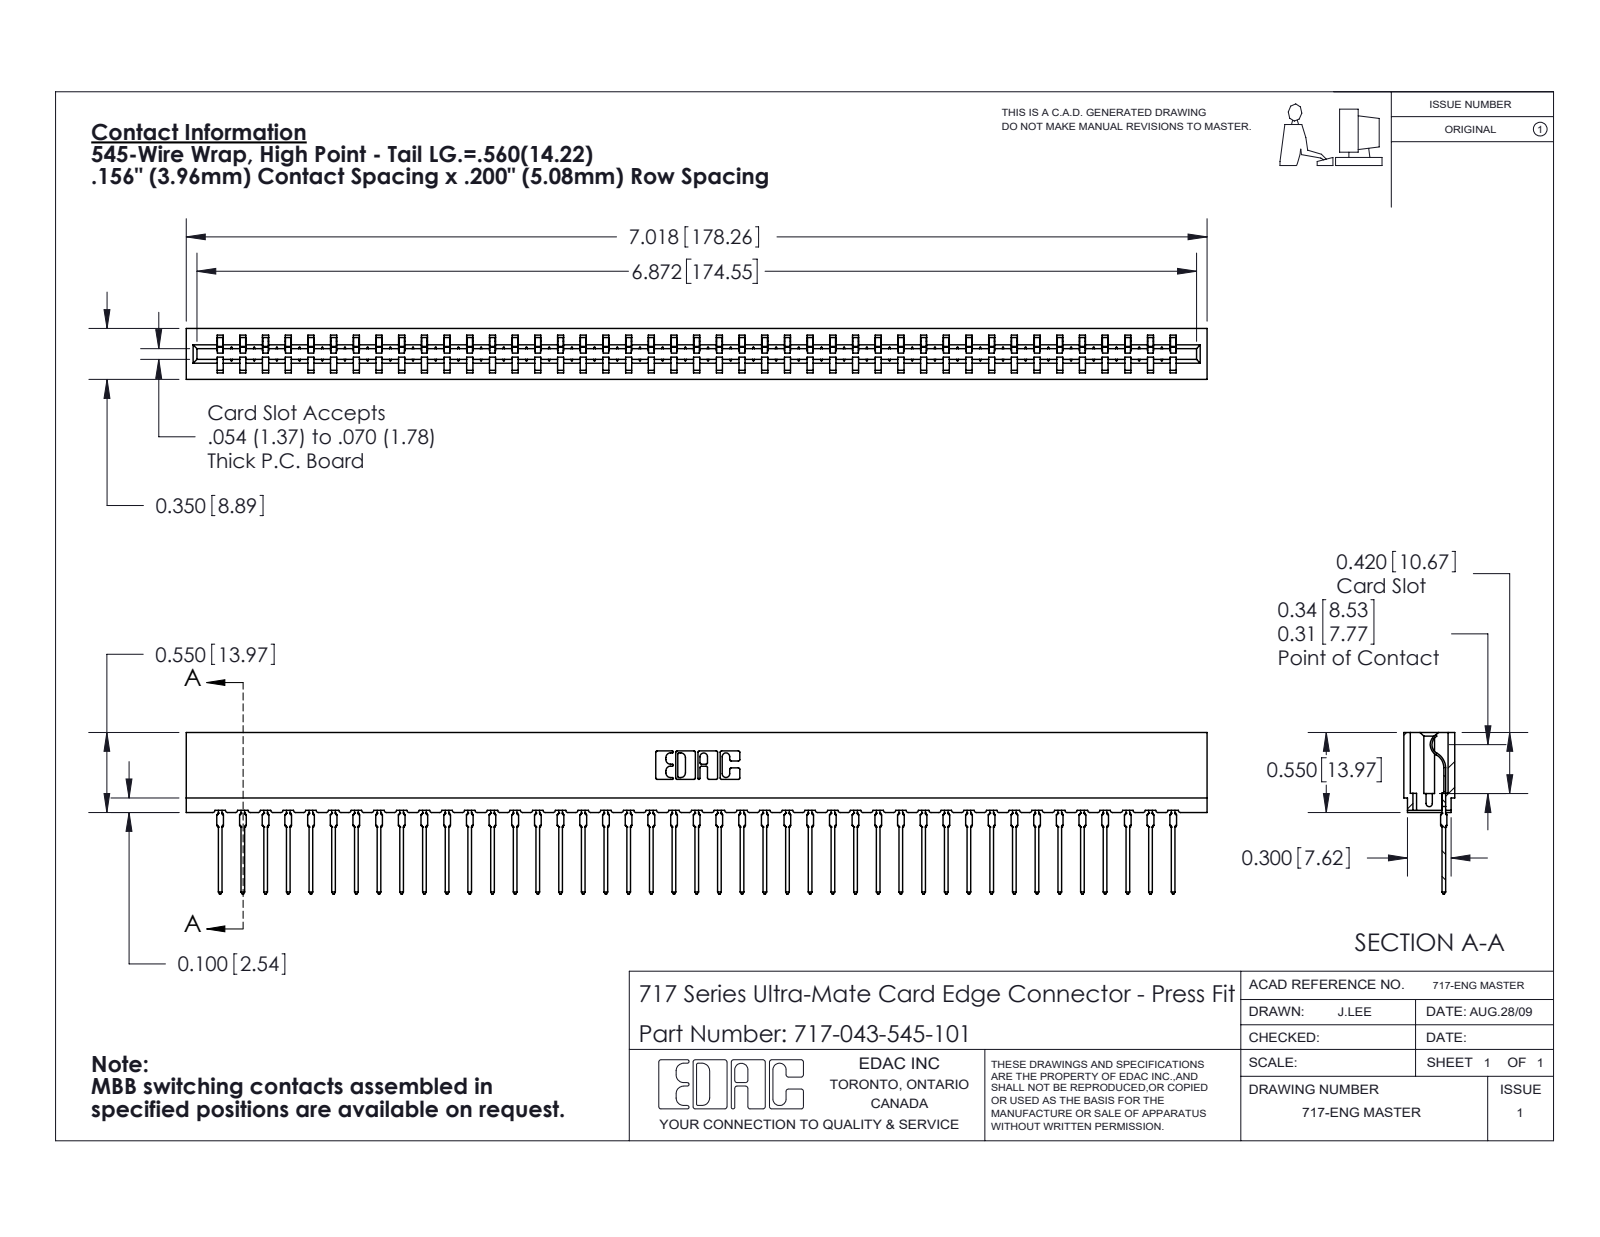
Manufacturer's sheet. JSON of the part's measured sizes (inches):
{"part_name": "717-043-545-101; 717 Part_Insulator Option - 06; 745-292-001_545", "step_written_by": "SolidWorks 2020 (CONFIG_CONTROL_DESIGN)", "units": "inches", "bodies": {"solids": 44, "faces": 4953, "planar": 2978, "cylindrical": 857, "other": 1118}, "overall_size": [7.018, 1.109, 0.35], "volume_in3": 0.926, "surface_area_in2": 34.09, "partial_cylinders_radius": [[0.015, 86], [0.021, 86], [0.01, 22], [0.007, 6], [0.031, 6], [0.005, 4], [0.011, 4], [0.026, 3]], "face_to_face_distances": [0.212, 0.138, 0.35, 0.063, 0.287, 0.076, 0.149, 0.074, 0.045, 0.305]}
